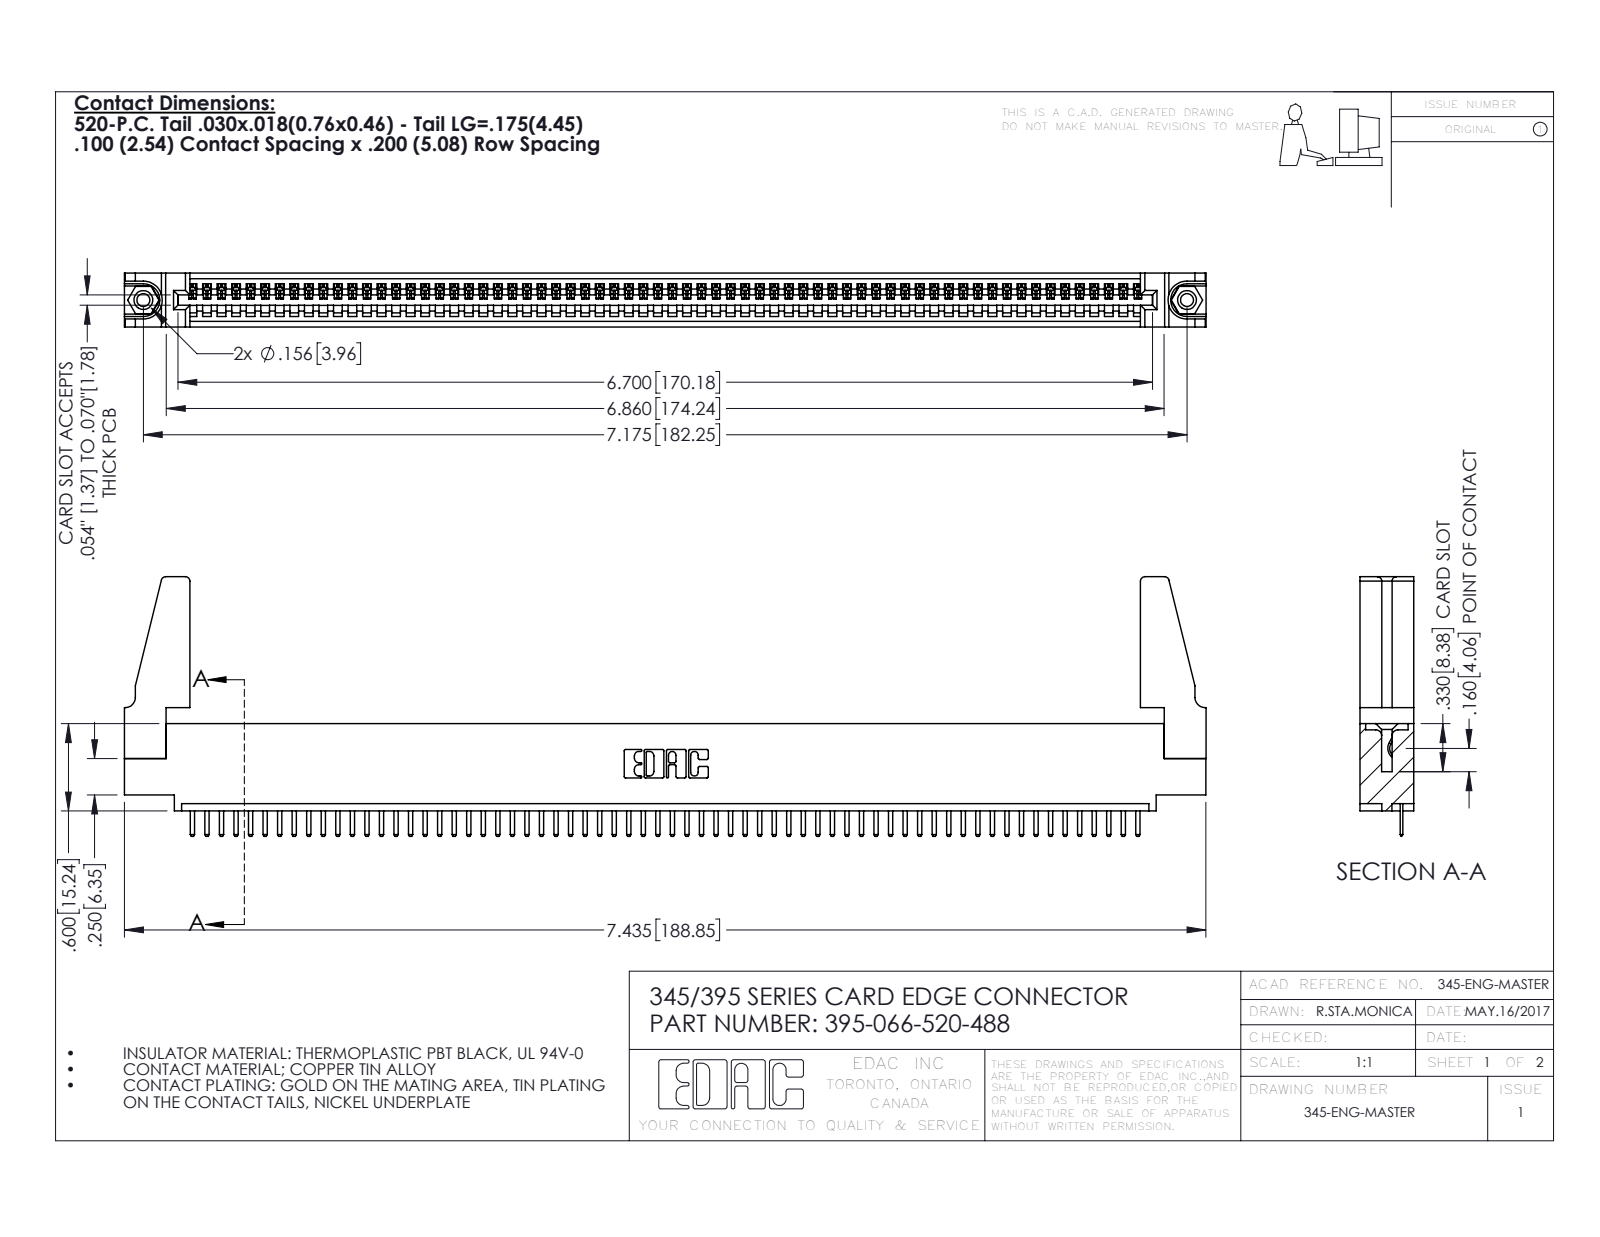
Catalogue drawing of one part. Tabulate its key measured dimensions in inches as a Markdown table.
| quantity | value |
| --- | --- |
| part name | 345-292-001_345-293-120; 345-220-078_345-220-088; 345-250-001_345-250-001-102; 395-066-520-488 (+1 more) |
| STEP written by | SolidWorks 2016 (CONFIG_CONTROL_DESIGN) |
| units | inches |
| bodies | 71 solids, 4346 faces (2928 planar, 1402 cylindrical, 16 other) |
| overall size | 7.436 × 1.785 × 0.37 |
| volume | 1.289 in³ |
| surface area | 41.33 in² |
| round holes (diameter × count) | 0.089 × 2, 0.125 × 2, 0.156 × 2, 0.064 × 1 |
| round bosses / shafts (diameter × count) | 0.155 × 2 |
| partial cylindrical surfaces (radius × count) | 0.01 × 134, 0.006 × 132, 0.01 × 22, 0.03 × 8, 0.007 × 6, 0.031 × 6, 0.026 × 3, 0.031 × 2 |
| main face-to-face distances | 0.072, 0.298, 0.37, 0.098, 0.272, 0.025, 0.2, 0.225, 0.072, 0.149 |
| hole center spacings | 0.27, 6.939, 7.175 |
